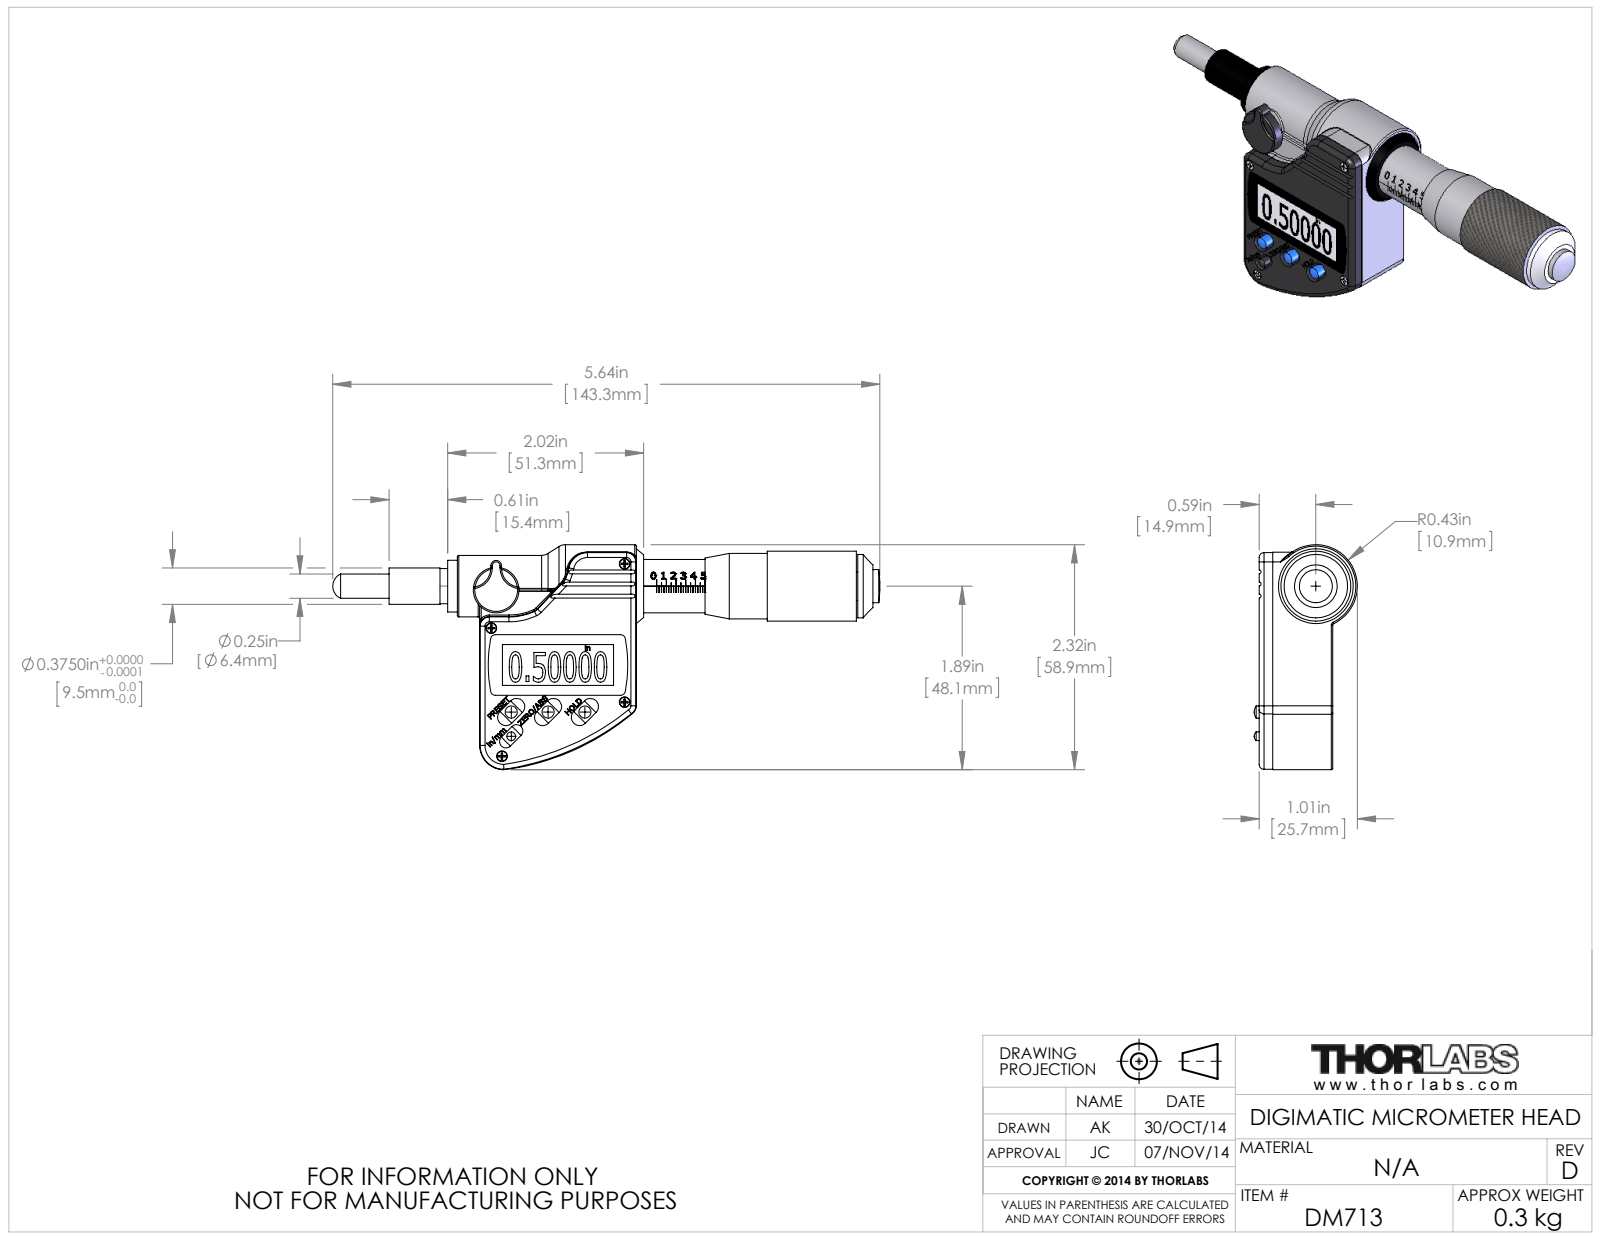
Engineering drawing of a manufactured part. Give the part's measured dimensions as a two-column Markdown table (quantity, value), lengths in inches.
| quantity | value |
| --- | --- |
| part name | 2774-E0W |
| STEP written by | SolidWorks 2007 (AUTOMOTIVE_DESIGN) |
| units | inches |
| bodies | 14 solids, 1125 faces (597 planar, 121 cylindrical, 407 other) |
| overall size | 5.641 × 2.32 × 1.063 |
| volume | 3.55 in³ |
| surface area | 33.46 in² |
| round holes (diameter × count) | 0.11 × 4, 0.55 × 1 |
| round bosses / shafts (diameter × count) | 0.1 × 4, 0.125 × 2, 0.72 × 1, 0.675 × 1, 0.654 × 1, 0.635 × 1, 0.535 × 1, 0.47 × 1 |
| partial cylindrical surfaces (radius × count) | 0.015 × 12, 0.05 × 9, 0.1 × 6, 0.02 × 3, 0.085 × 3, 0.095 × 3, 0.2 × 3, 1.415 × 2 |
| main face-to-face distances | 0.62, 0.14, 0.76, 1.615, 0.55, 0.07, 0.21, 0.759, 0.21, 0.14 |
| hole center spacings | 1.324, 1.382, 1.426, 1.526, 1.572, 2.352 |
